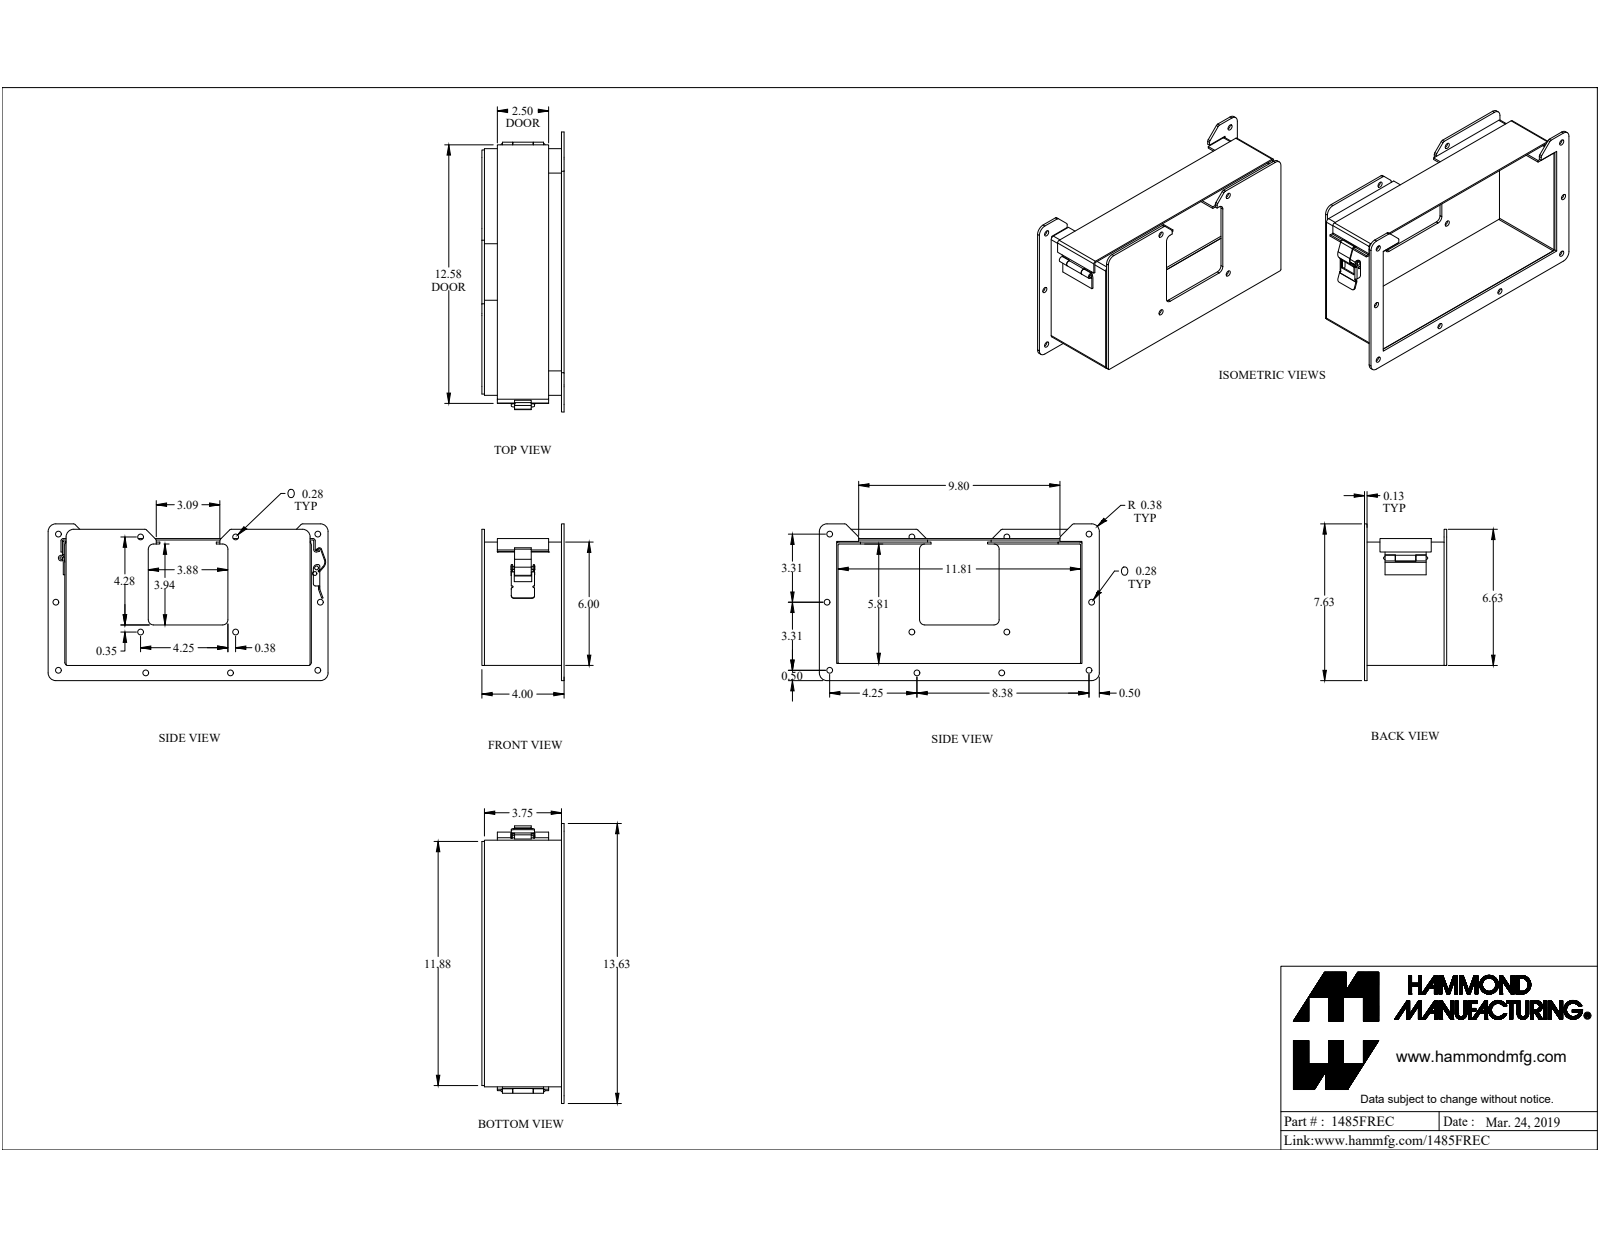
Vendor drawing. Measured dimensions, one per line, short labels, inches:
name: 1485FREC
written by: SolidWorks 2019 (CONFIG_CONTROL_DESIGN)
unit: in
bodies: 10 solids, 253 faces (146 planar, 105 cylindrical, 2 other)
size: 13.625 × 7.625 × 4
volume: 23.98 in³; area: 499.8 in²
holes: 12× ⌀0.281, 1× ⌀0.125, 1× ⌀0.13, 1× ⌀0.164
bosses: 2× ⌀0.187, 1× ⌀0.275, 1× ⌀0.156, 1× ⌀0.125, 1× ⌀0.125
rounds: 11× R0.125, 7× R0.016, 6× R0.375, 4× R0.048, 4× R0.143, 4× R0.25, 3× R0.035, 3× R0.036
face distances: 0.095, 0.125, 11.905, 5.905, 0.072, 6.1, 6.172, 6.005, 6.077, 3.875
hole spacings: 4.625, 13.173, 2.003, 3.315, 3.315, 4.002, 4.252, 4.372
